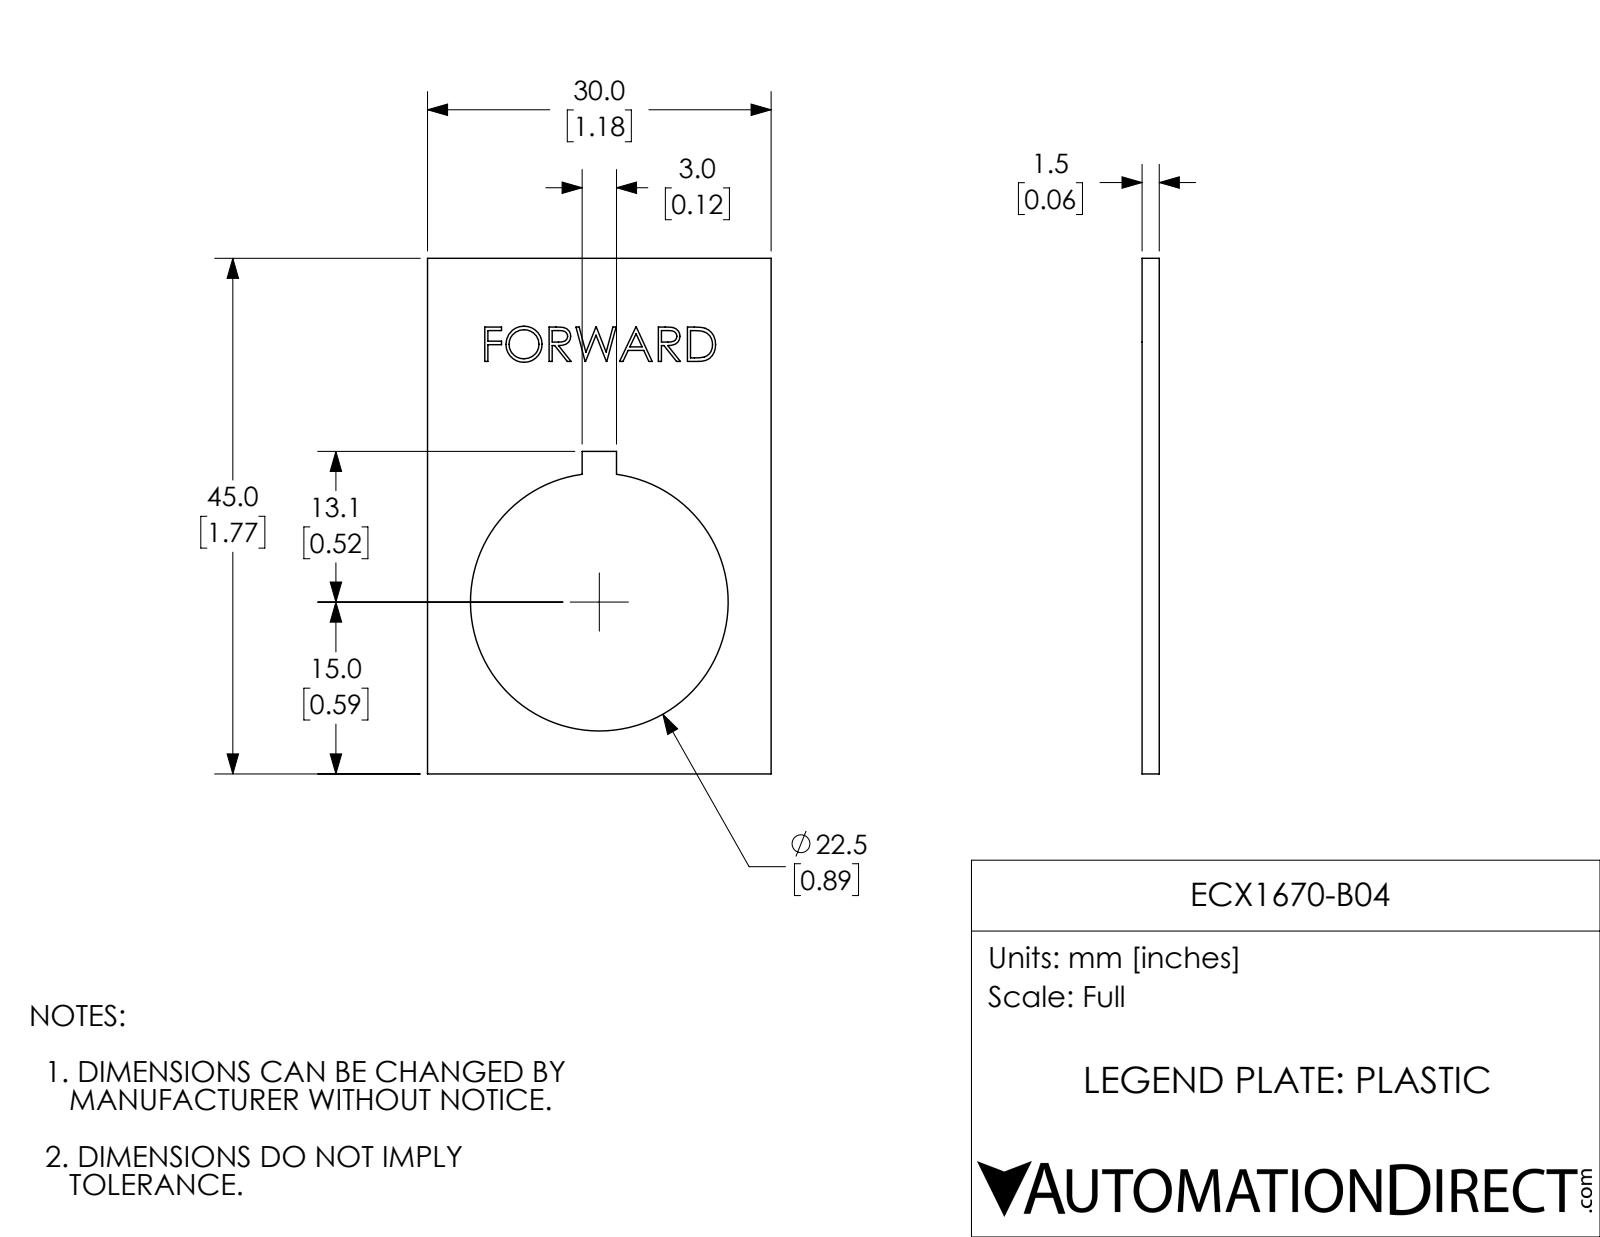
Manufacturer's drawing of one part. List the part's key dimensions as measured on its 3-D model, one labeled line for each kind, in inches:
Part name (STEP PRODUCT): ECX1670-B04
STEP written by: SolidWorks 2017 (AUTOMOTIVE_DESIGN)
Units: inches
Bodies: 1 solid, 111 faces (83 planar, 3 cylindrical, 25 other)
Overall size (bounding box): 1.772 × 1.181 × 0.059
Volume: 0.087 in³ · Surface area: 3.461 in²
Round holes (diameter × count): ⌀0.886 ×1
Main face-to-face distances: 0.059, 1.181, 1.772, 0.058, 0.65, 0.531, 1.108, 0.663, 0.118, 0.221
